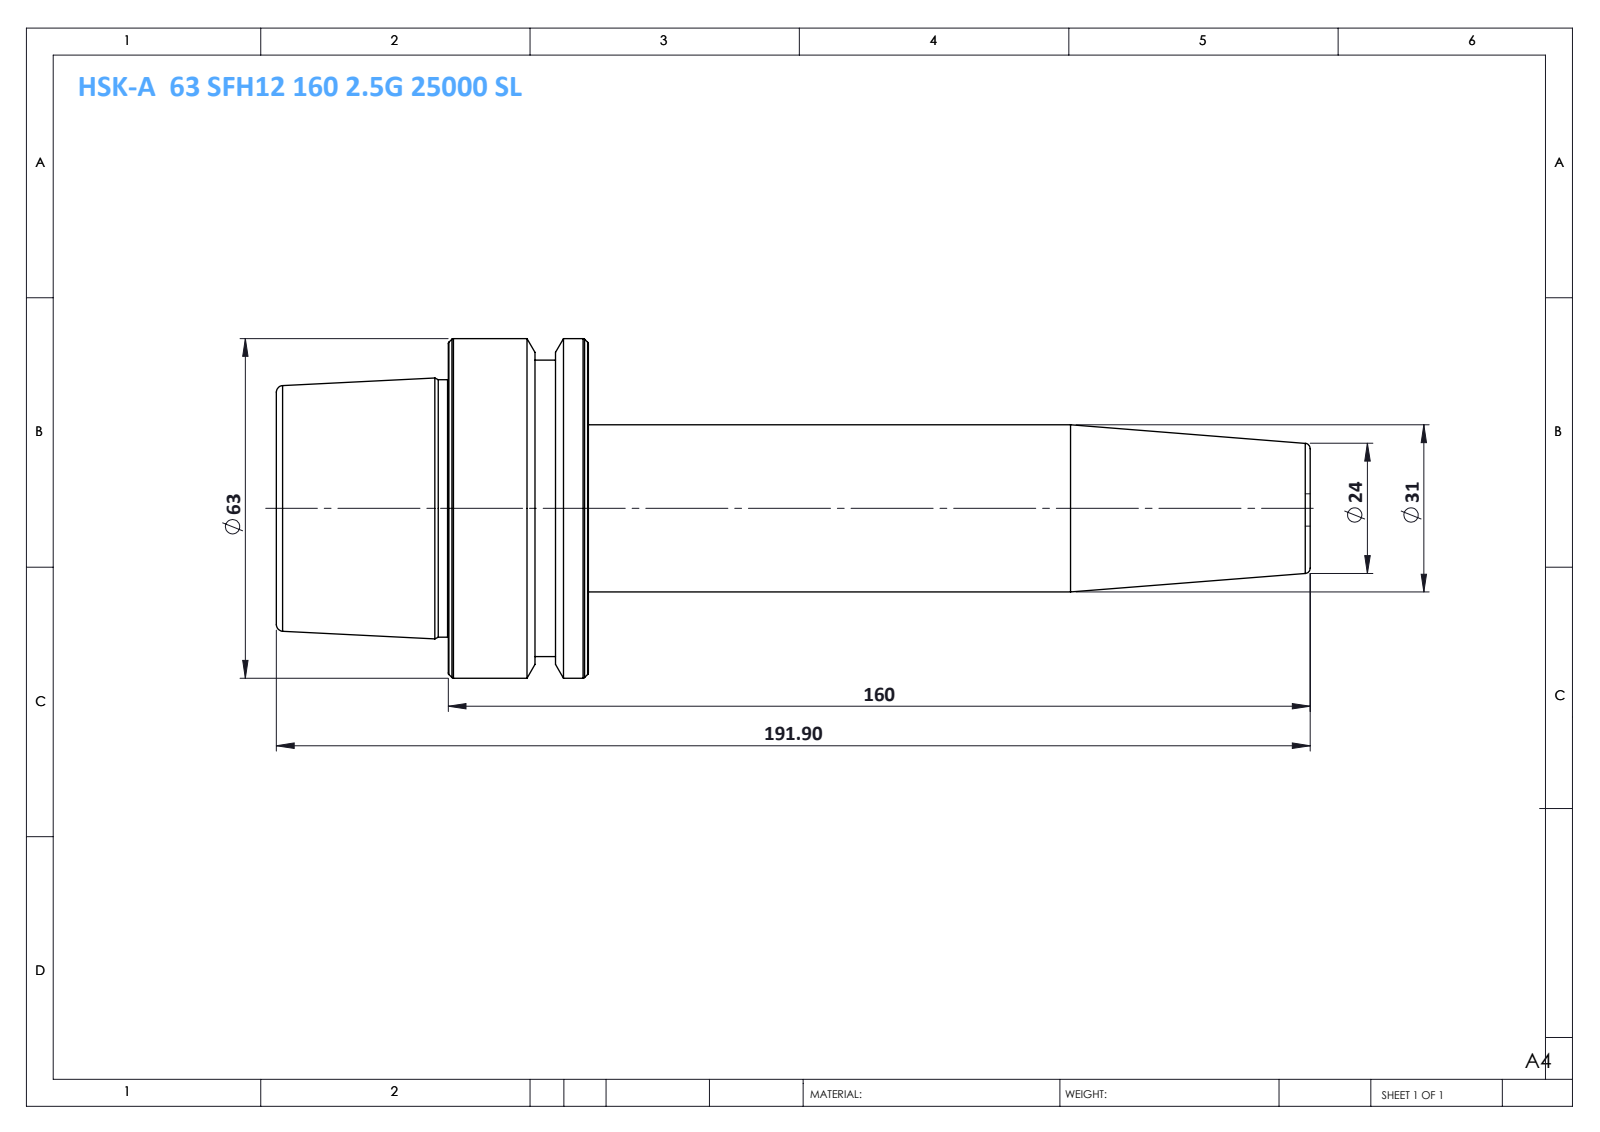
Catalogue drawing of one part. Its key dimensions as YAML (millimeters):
part_name: "HSK-A 63 SFH12 160 2.5G 25000 SL"
step_written_by: "SolidWorks 2014 (CONFIG_CONTROL_DESIGN)"
units: millimeters
bodies: {solids: 1, faces: 46, planar: 6, cylindrical: 10, other: 30}
overall_size: [191.9, 63, 63]
volume: 226713
surface_area: 28892
round_bosses_or_shafts:
  - {diameter: 63, count: 1}
  - {diameter: 55, count: 1}
  - {diameter: 47.78, count: 1}
  - {diameter: 31, count: 1}
face_to_face_distances: [57.9, 26, 31.9, 134, 160, 191.9, 140.1, 6.1, 19.9, 51.8]
